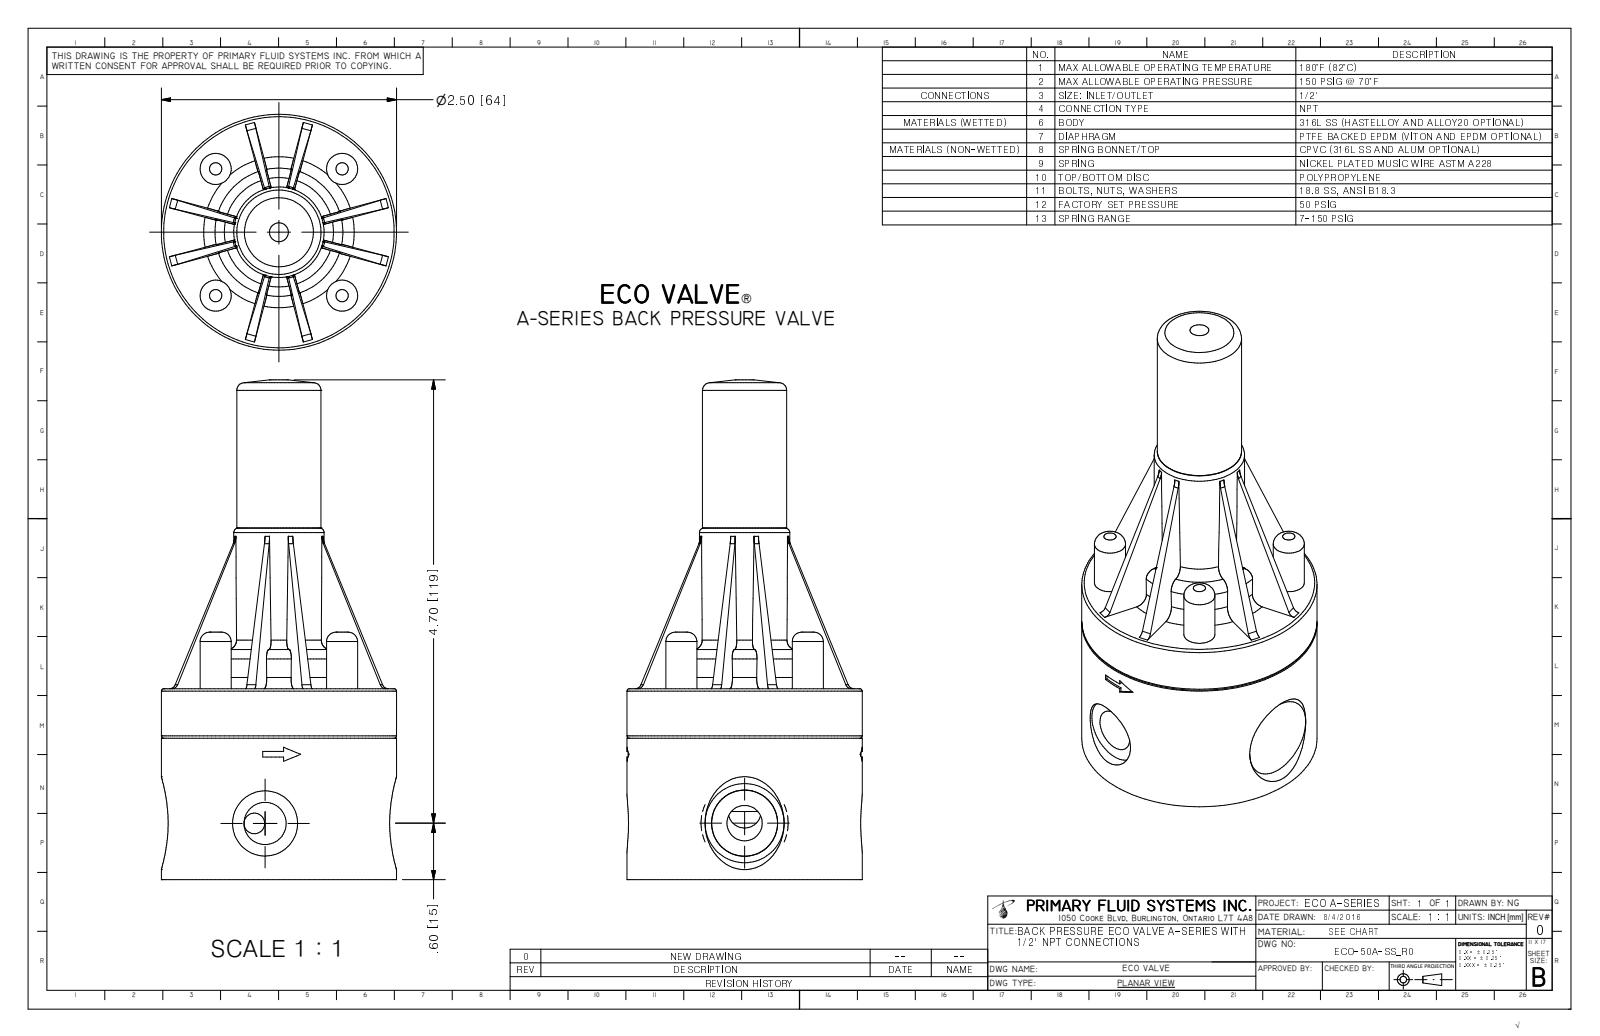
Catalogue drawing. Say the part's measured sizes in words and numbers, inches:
The part is named "ECO-50A-SS_R0". Its 3-D file was written by "Autodesk Inventor 2009 (AUTOMOTIVE_DESIGN)". It is 1 solid with 208 faces: 97 planar, 50 cylindrical and 61 other. Overall it measures 5.3 by 2.5 by 2.5 inches. Its volume is 12.01 cubic inches and its surface area 61.01 square inches. Round holes: 4 of diameter 0.23, 4 of diameter 0.256, 4 of diameter 0.257, 4 of diameter 0.4, 1 of diameter 0.218, 1 of diameter 0.448, 1 of diameter 0.691. Round bosses or shafts: 4 of diameter 0.33, 4 of diameter 0.256, 1 of diameter 2.5, 1 of diameter 1.36, 1 of diameter 0.96, 1 of diameter 0.895. Partial cylindrical surfaces (rounded edges, fillets, slot ends): 8 of radius 0.07, 1 of radius 1.23. The main face-to-face distances are 2.025, 1.75, 0.27, 1.254, 1.755, 0.275, 0.15, 0.12, 0.125, 1.875. The hole center spacings are 1.344, 1.344, 1.343, 1.9, 1.901, 1.344, 1.9, 0.114.
